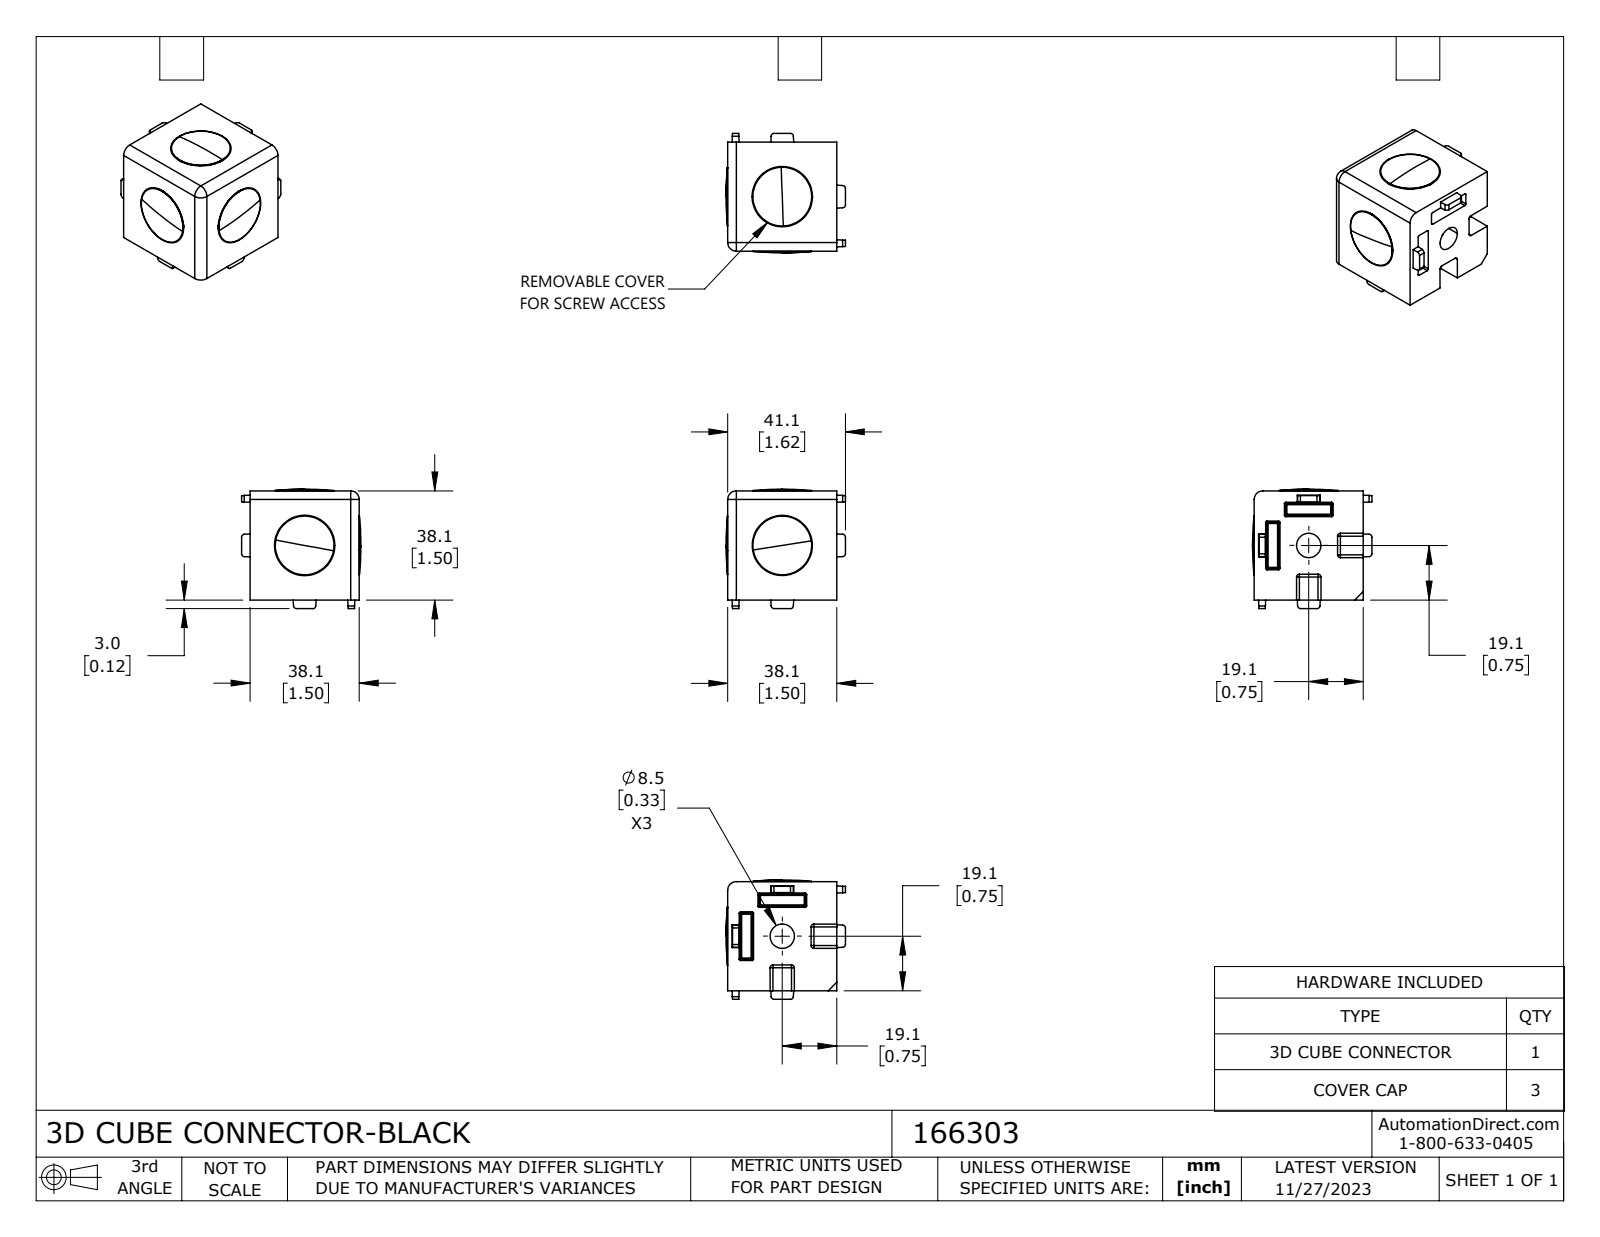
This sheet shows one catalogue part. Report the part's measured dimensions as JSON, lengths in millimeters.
{"part_name": "166303", "step_written_by": "SolidWorks 2023 (CONFIG_CONTROL_DESIGN)", "units": "millimeters", "bodies": {"solids": 4, "faces": 316, "planar": 103, "cylindrical": 111, "other": 102}, "overall_size": [41.7, 41.68, 41.68], "volume_mm3": 35149, "surface_area_mm2": 17157, "round_holes": [[8.5, 3]], "round_bosses_or_shafts": [[16.8, 3]], "partial_cylinders_radius": [[0.5, 48], [1, 27], [1.8, 18], [3, 3]], "face_to_face_distances": [38.1, 0.42, 37.68, 32.1, 6, 3, 9, 14.8, 23.3, 29.1]}
